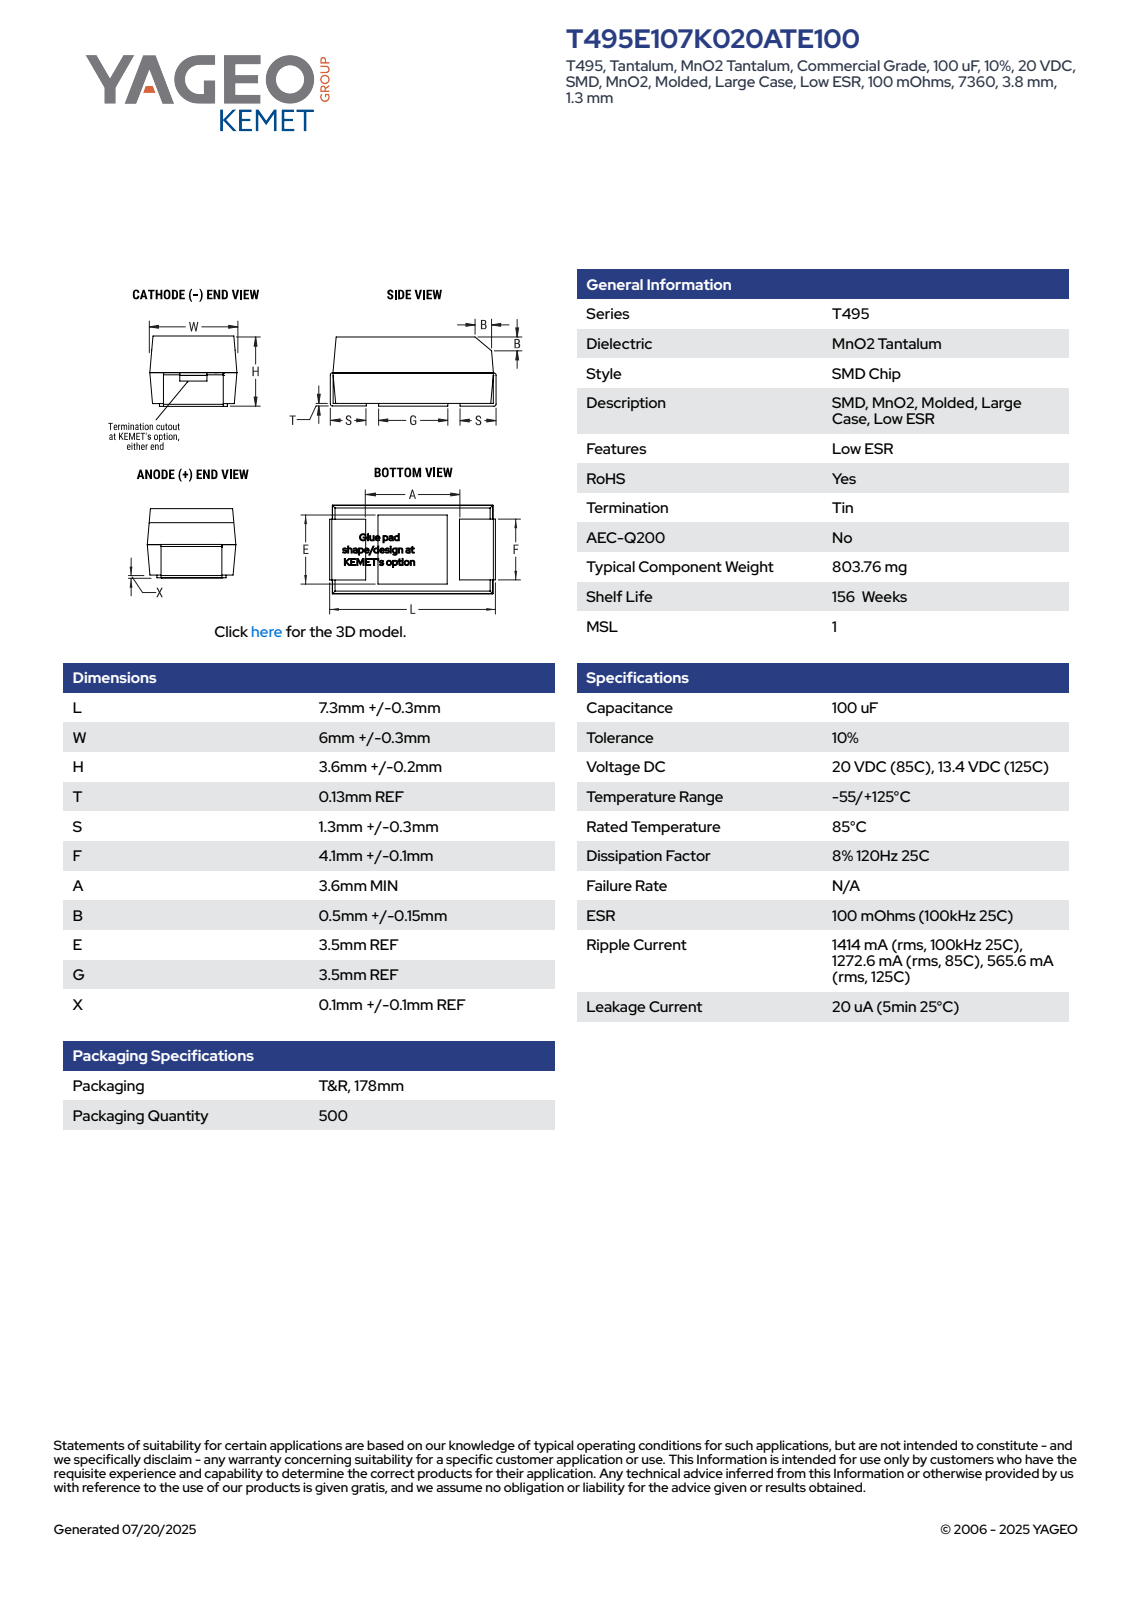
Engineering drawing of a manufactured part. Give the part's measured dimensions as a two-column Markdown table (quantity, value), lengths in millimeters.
| quantity | value |
| --- | --- |
| part name | CTSM_TCM2NKRP_7360_L7.6W6.3H3.8T0.13S1.3F4.2A3.6B0.65E3.5G3.5X0.2 |
| STEP written by | SolidWorks 2014 (AUTOMOTIVE_DESIGN) |
| units | millimeters |
| bodies | 4 solids, 94 faces (90 planar, 4 cylindrical, 0 other) |
| overall size | 7.6 × 6.3 × 3.81 |
| volume | 158 mm³ |
| surface area | 227 mm² |
| partial cylindrical surfaces (radius × count) | 0.1 × 4 |
| main face-to-face distances | 3.8, 3.6, 7.47, 6.19, 6.2, 3.67, 7.6, 7.34, 2.05, 5.55 |
